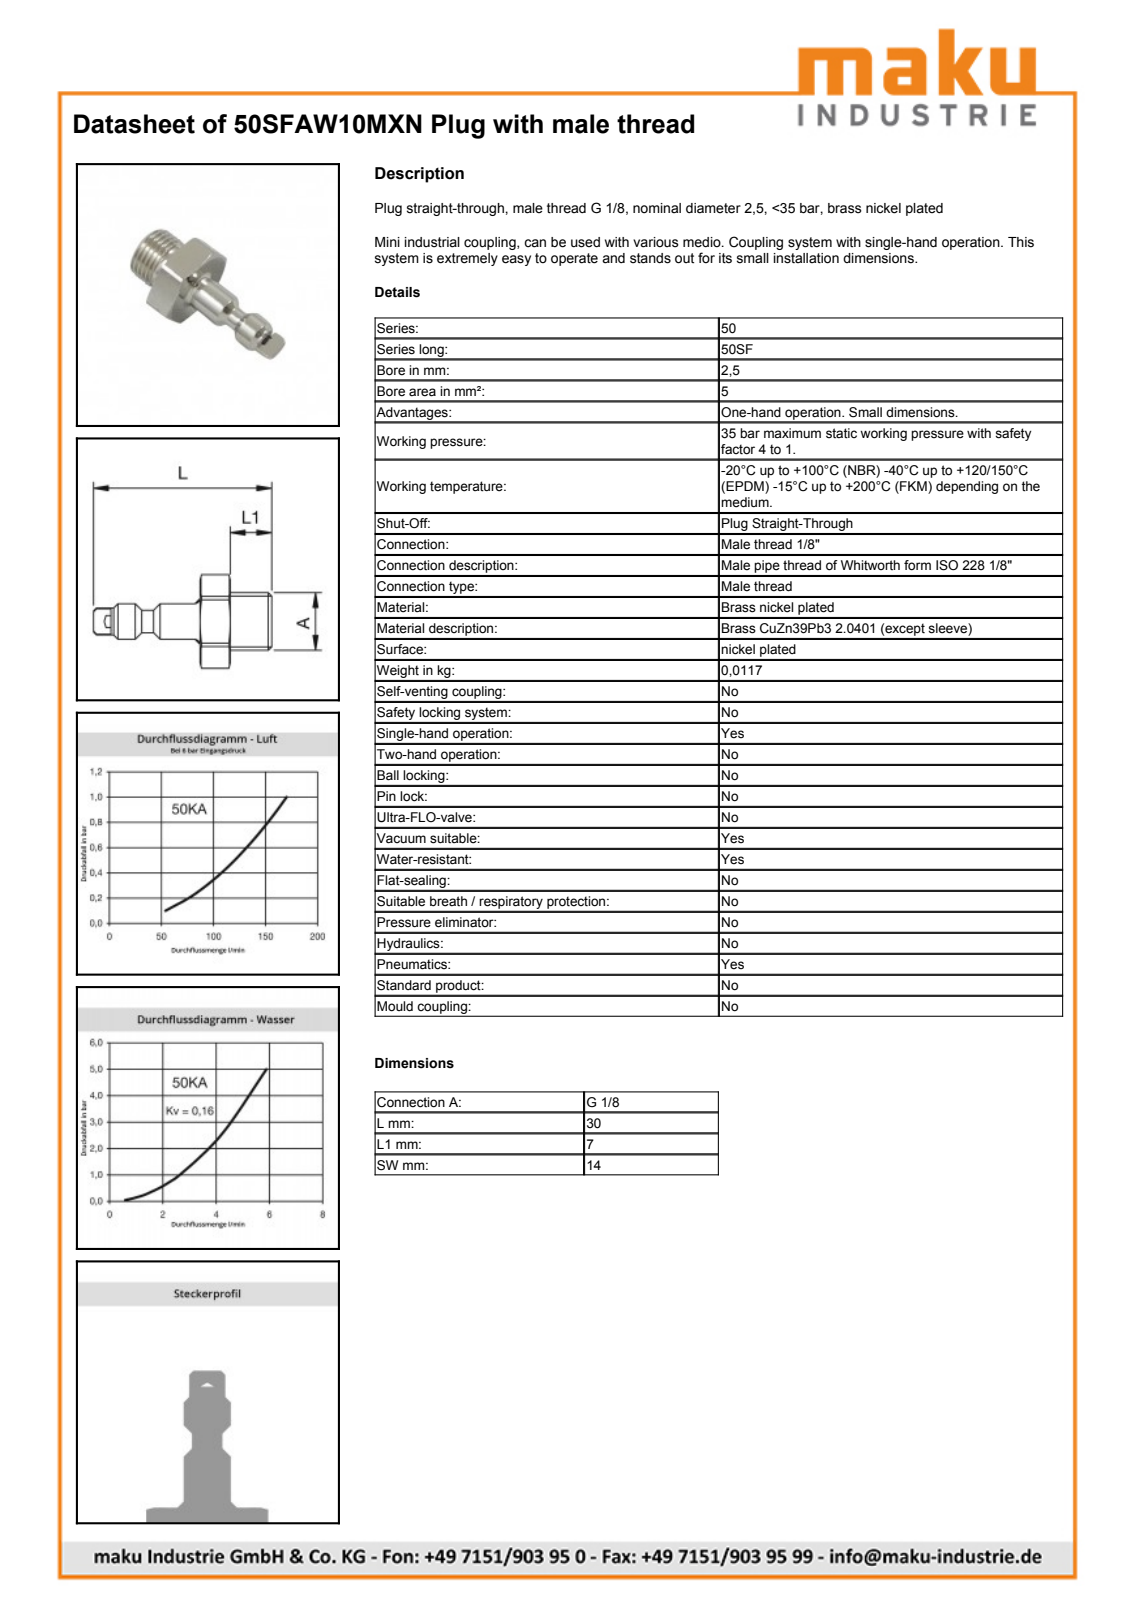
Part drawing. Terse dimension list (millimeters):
name: D109119
written by: Autodesk Inventor 2013 (AUTOMOTIVE_DESIGN)
unit: mm
bodies: 1 solid, 51 faces (14 planar, 13 cylindrical, 24 other)
size: 30 × 15.8 × 14
volume: 1 453 mm³; area: 1 353 mm²
holes: 1× ⌀2.5, 1× ⌀4
bosses: 1× ⌀9.73, 1× ⌀6, 1× ⌀4.55, 1× ⌀3.8
rounds: 1× R7.9
face distances: 14, 5, 12, 7, 6.25, 7.75, 1.5, 15.05, 20.05, 27.05
